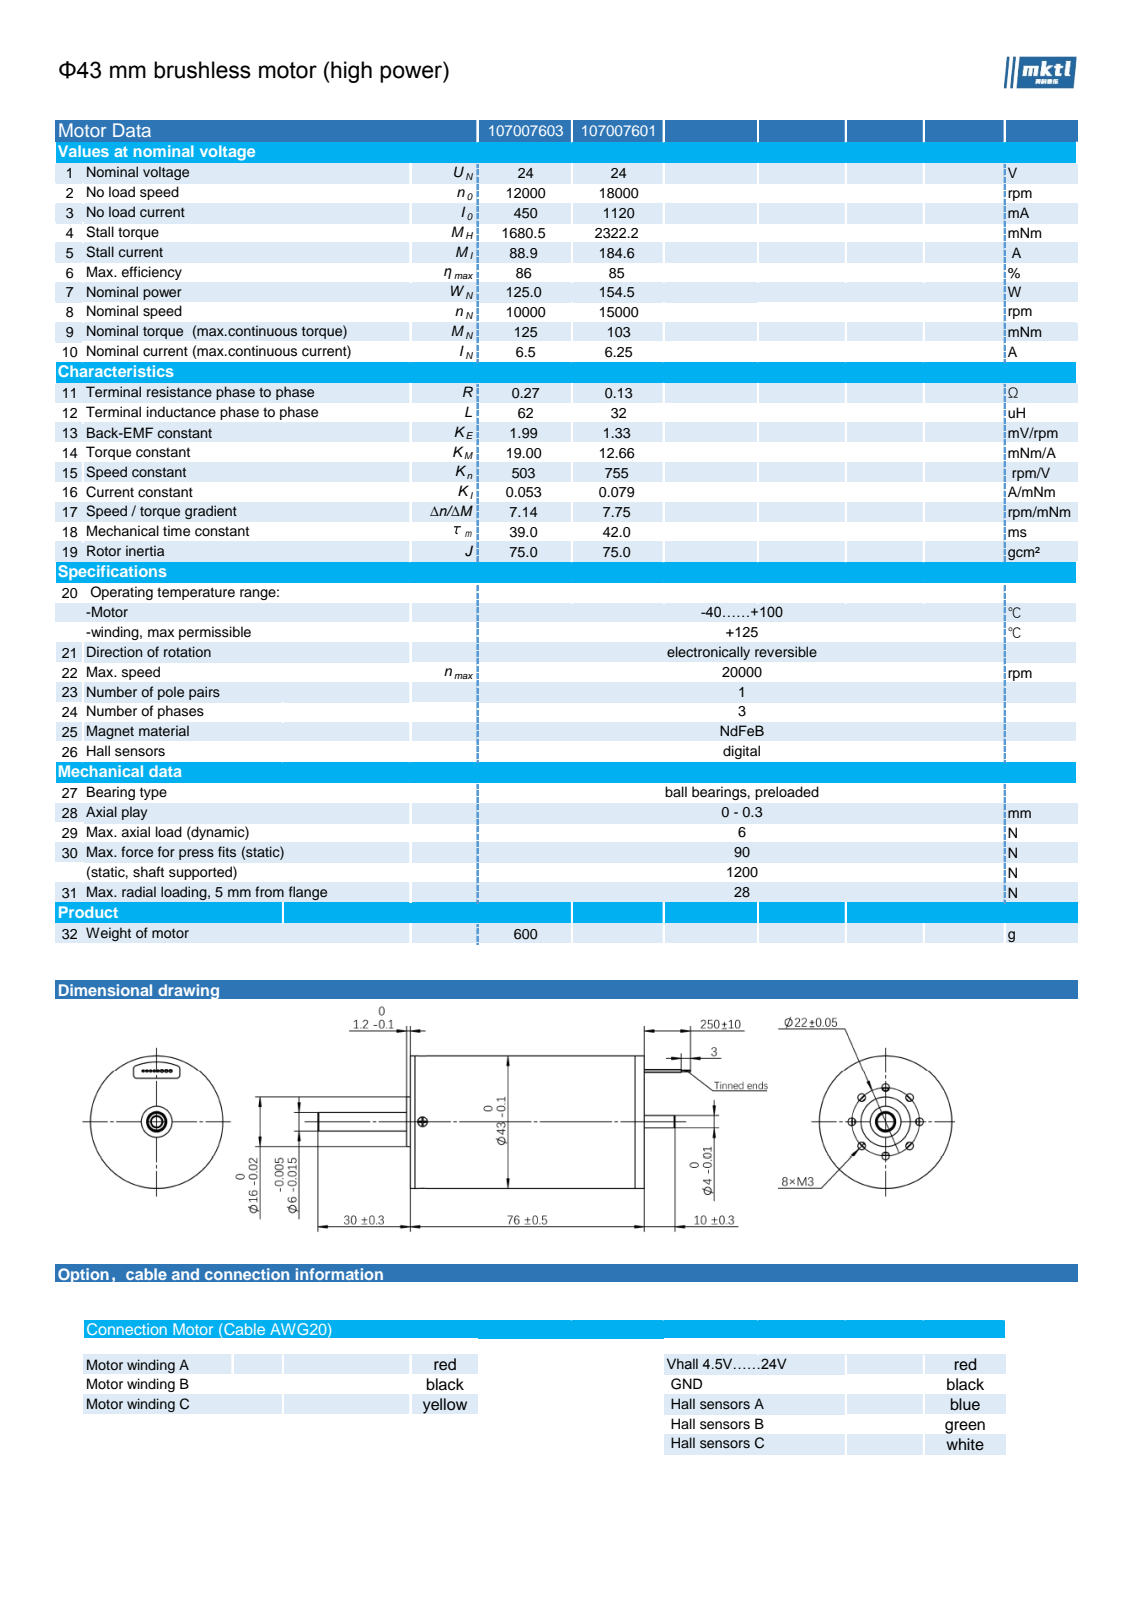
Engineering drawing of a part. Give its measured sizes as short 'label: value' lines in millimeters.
name: 107007601
written by: SolidWorks 2025 (AUTOMOTIVE_DESIGN)
unit: mm
bodies: 336 solids, 3050 faces (1137 planar, 1789 cylindrical, 124 other)
size: 121 × 43 × 43
volume: 100 995 mm³; area: 445 960 mm²
holes: 9× ⌀1, 8× ⌀1.5, 8× ⌀2.5, 5× ⌀0.85, 5× ⌀1.2, 3× ⌀2.1, 3× ⌀2.2, 3× ⌀3, 2× ⌀3.1, 1× ⌀6, 1× ⌀10.5, 1× ⌀12
bosses: 5× ⌀0.6, 3× ⌀4, 3× ⌀1.6, 3× ⌀0.8, 3× ⌀0.5, 2× ⌀2.8, 2× ⌀1.4, 2× ⌀1.3
rounds: 24× R0.1, 21× R1, 3× R0.3, 2× R0.5, 1× R2, 1× R6.1, 1× R6.6, 1× R7.15
face distances: 0.4, 0.6, 0.8, 1, 1.2, 1.4, 1.6, 1.8, 2, 2.2
hole spacings: 8.42, 11, 15.56, 20.33, 2, 26.4, 6, 16
